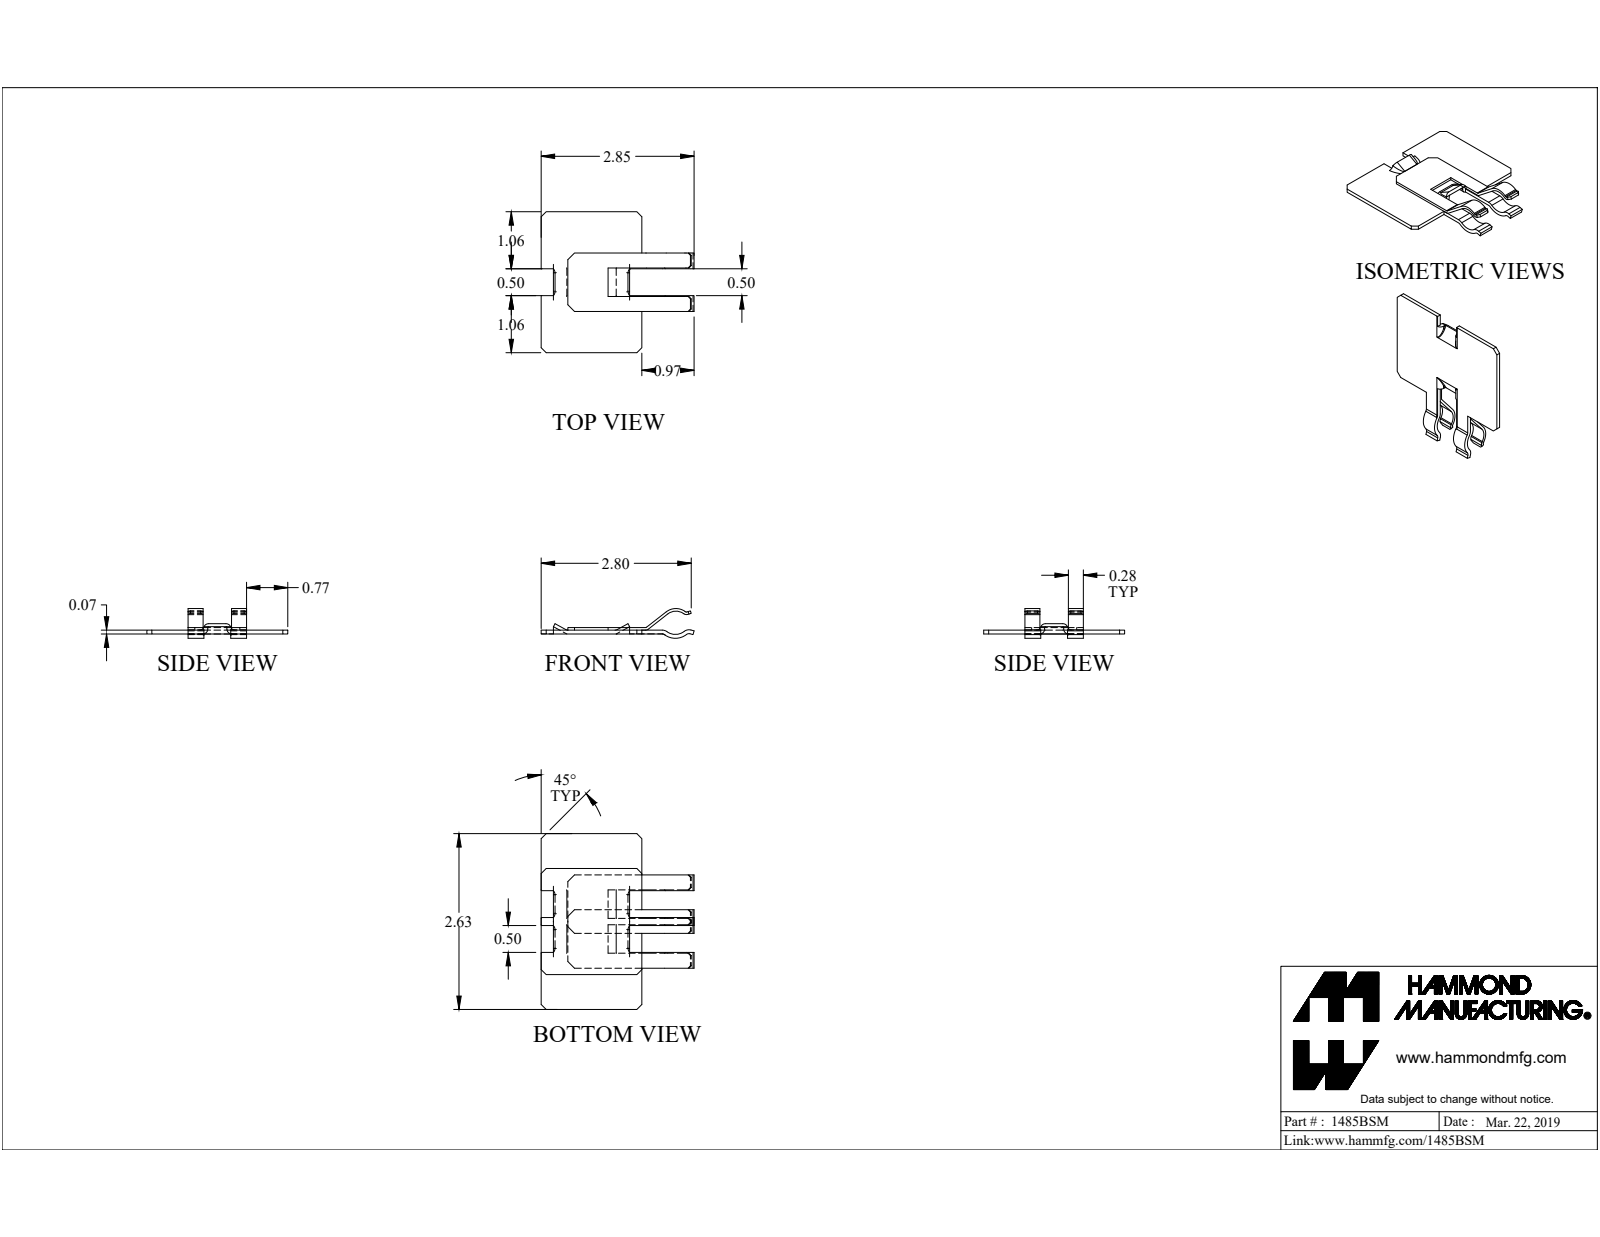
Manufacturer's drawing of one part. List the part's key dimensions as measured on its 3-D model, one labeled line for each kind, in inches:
Part name (STEP PRODUCT): 1485BSM
STEP written by: SolidWorks 2019 (CONFIG_CONTROL_DESIGN)
Units: inches
Bodies: 4 solids, 127 faces (79 planar, 38 cylindrical, 10 other)
Overall size (bounding box): 2.848 × 2.625 × 0.599
Volume: 0.956 in³ · Surface area: 25.14 in²
Partial cylindrical surfaces — rounded edges, fillets, slot ends (radius × count): R0.09 ×8, R0.015 ×4, R0.072 ×3, R0.144 ×2, R0.024 ×1, R0.03 ×1, R0.078 ×1, R0.245 ×1
Main face-to-face distances: 0.072, 0.125, 0.197, 0.048, 0.245, 0.12, 0.75, 1.043, 0.768, 1.857
